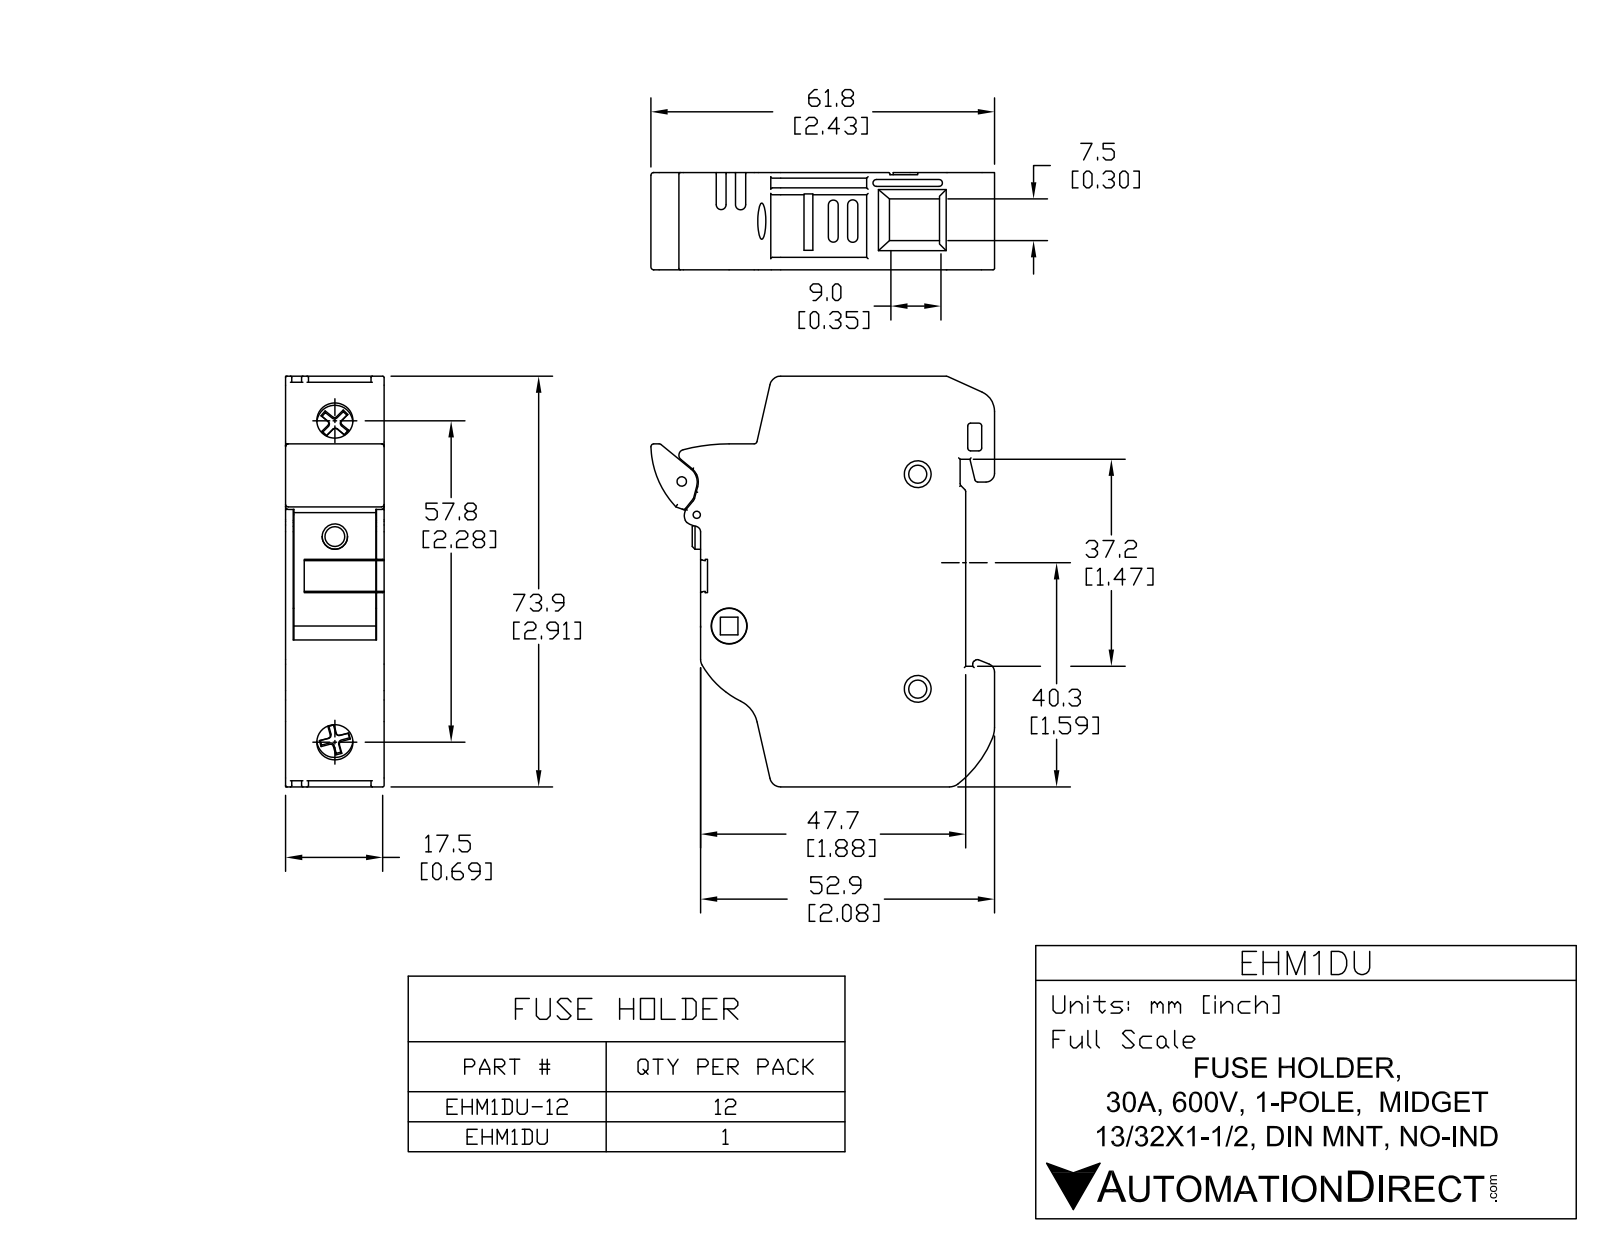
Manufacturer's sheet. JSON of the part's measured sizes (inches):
{"part_name": "EHM1DU", "step_written_by": "SolidWorks 2011 (AUTOMOTIVE_DESIGN)", "units": "inches", "bodies": {"solids": 1, "faces": 589, "planar": 245, "cylindrical": 196, "other": 148}, "overall_size": [2.909, 2.434, 0.689], "volume_in3": 3.217, "surface_area_in2": 30.28, "round_holes": [[0.128, 2], [0.19, 2], [0.256, 2], [0.051, 1], [0.067, 1], [0.255, 1]], "round_bosses_or_shafts": [[0.25, 1]], "partial_cylinders_radius": [[0.01, 60], [0.02, 21], [0.079, 10], [0.02, 9], [0.039, 7], [0.024, 4], [0.035, 3], [0.036, 3]], "face_to_face_distances": [0.689, 0.049, 0.062, 0.64, 0.054, 0.635, 0.586, 1.083, 1.145, 0.903], "hole_center_spacings": [0.259, 0.82, 1.077, 1.408, 1.409, 1.52, 1.522, 1.592]}
